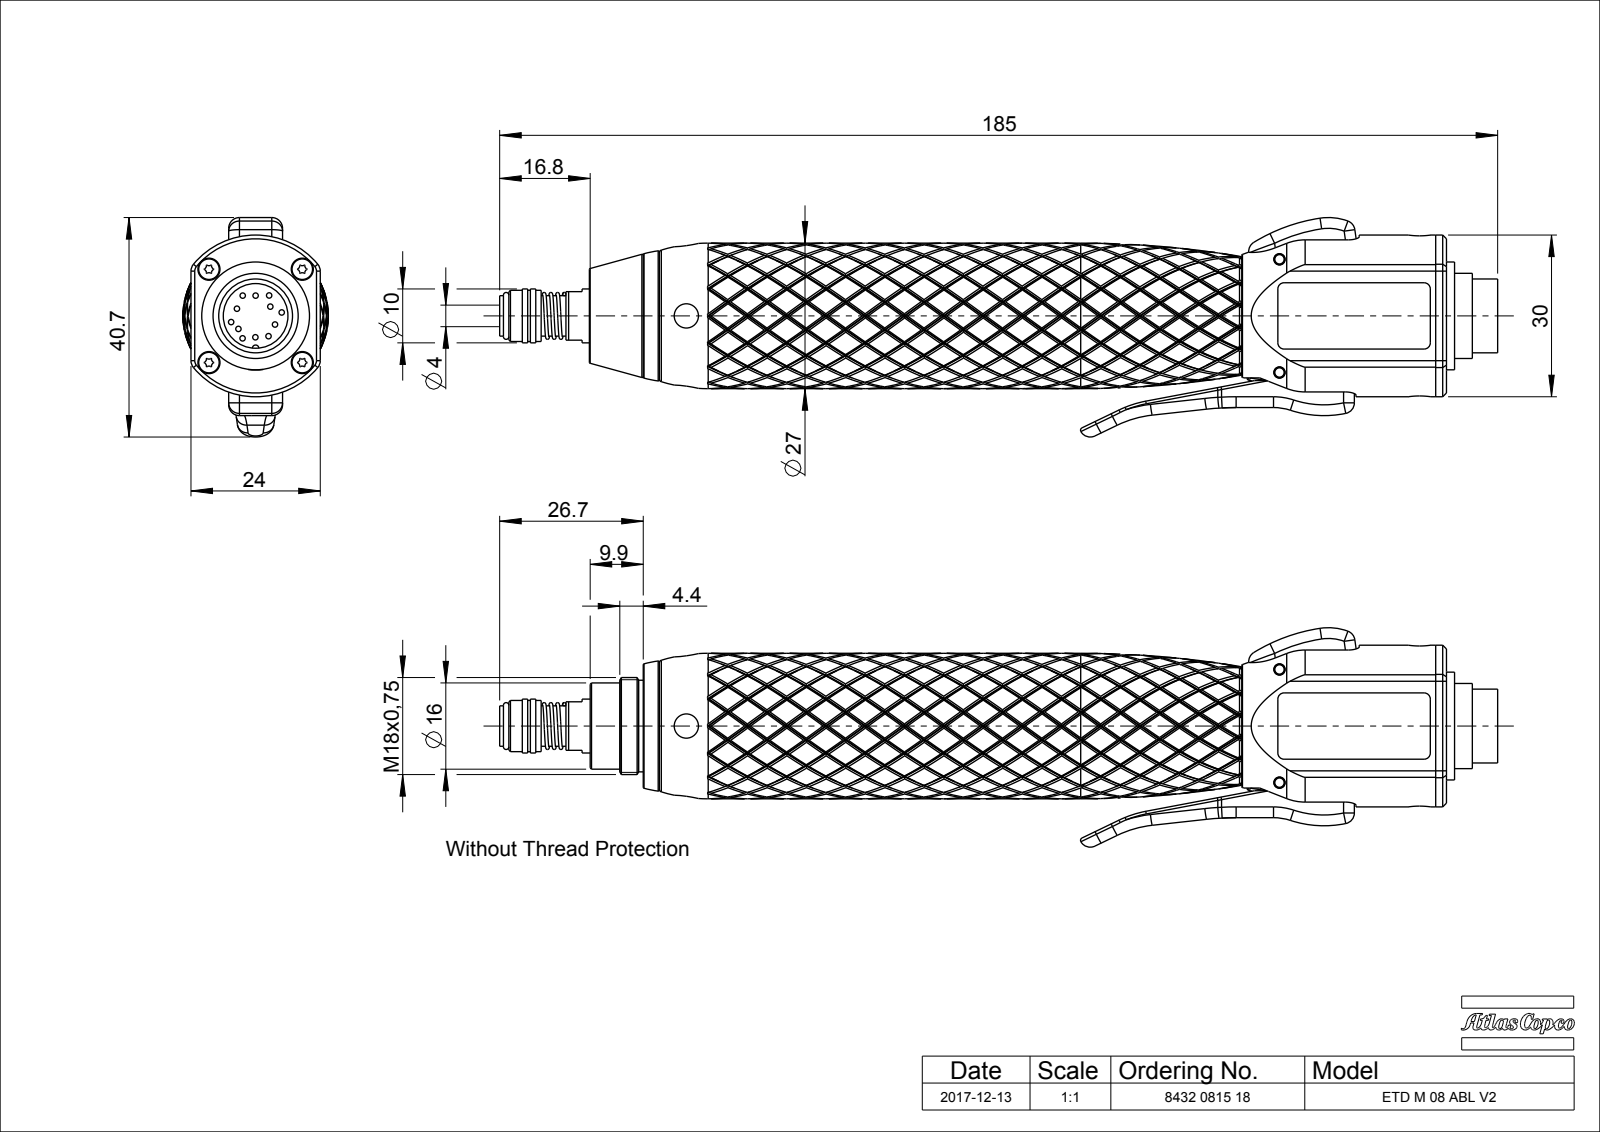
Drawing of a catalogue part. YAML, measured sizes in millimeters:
part_name: "4216137002; 4216151600; 0219110036; 4216151780_SPEC (+8 more)"
step_written_by: "PRO/ENGINEER BY PARAMETRIC TECHNOLOGY CORPORATION, 2013410 (CONFIG_CONTROL_DESIGN)"
units: millimeters
bodies: {solids: 22, faces: 3125, planar: 315, cylindrical: 736, other: 2074}
overall_size: [185.25, 40.72, 27]
volume: 44983
surface_area: 47576
round_holes:
  - {diameter: 2.1, count: 10}
  - {diameter: 1.6, count: 5}
  - {diameter: 2, count: 3}
  - {diameter: 4, count: 3}
  - {diameter: 4.5, count: 2}
  - {diameter: 1.73, count: 1}
  - {diameter: 1.8, count: 1}
  - {diameter: 3, count: 1}
  - {diameter: 3.2, count: 1}
  - {diameter: 4.2, count: 1}
  - {diameter: 7.55, count: 1}
  - {diameter: 8.2, count: 1}
round_bosses_or_shafts:
  - {diameter: 1, count: 12}
  - {diameter: 2, count: 5}
  - {diameter: 3.8, count: 4}
  - {diameter: 27, count: 1}
  - {diameter: 20, count: 1}
  - {diameter: 19.9, count: 1}
  - {diameter: 19, count: 1}
  - {diameter: 18.3, count: 1}
partial_cylinders:
  - {radius: 2, count: 26}
  - {radius: 0.1, count: 24}
  - {radius: 0.53, count: 24}
  - {radius: 5, count: 11}
  - {radius: 1.15, count: 8}
  - {radius: 0.5, count: 6}
  - {radius: 10, count: 3}
  - {radius: 20, count: 3}
face_to_face_distances: [23, 2, 3, 23.8, 1.5, 0.8, 23.6, 0.6, 3.5, 16.8]
hole_center_spacings: [12.25, 17.32, 11.85, 24.49, 51.58, 110.6, 117.85, 11.71]
